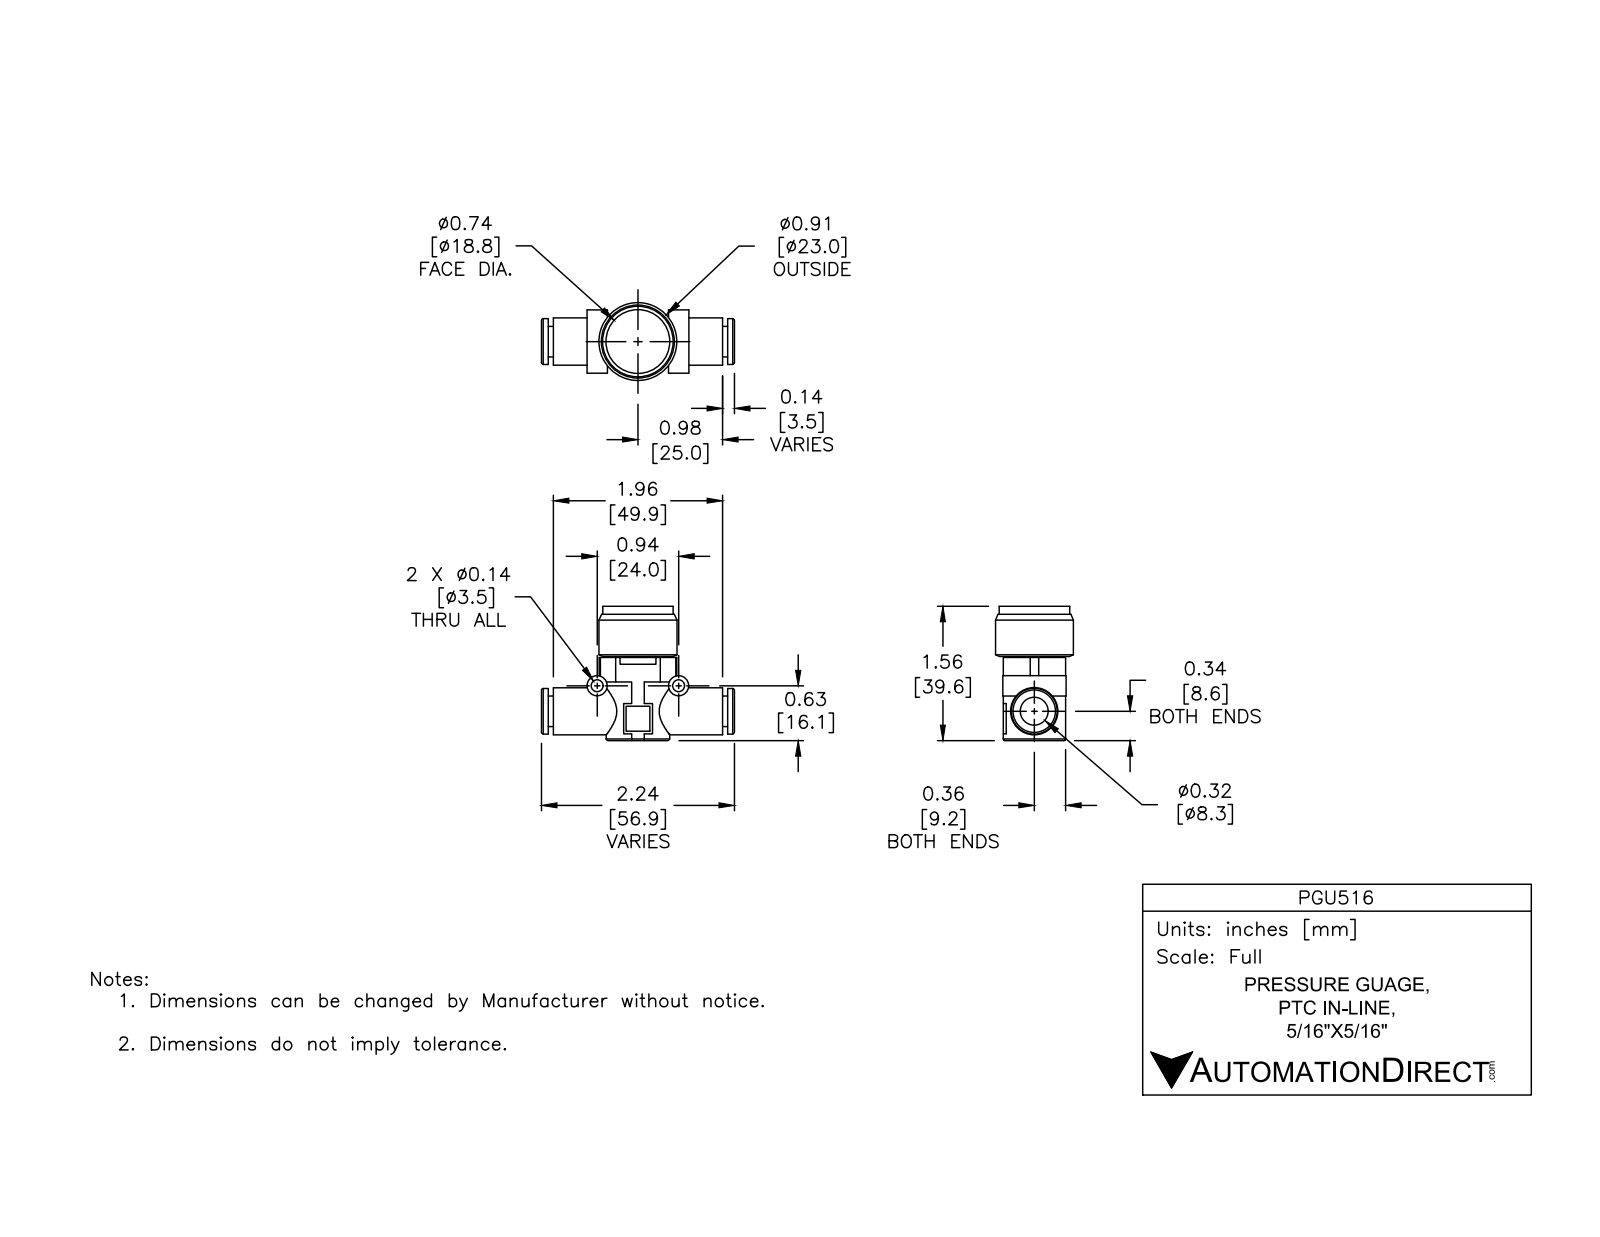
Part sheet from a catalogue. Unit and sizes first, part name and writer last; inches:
Units: inches
Overall size (bounding box): 2.24 × 1.559 × 0.906
Round holes (diameter × count): ⌀0.138 ×2, ⌀0.325 ×1, ⌀0.354 ×1, ⌀0.738 ×1, ⌀0.787 ×1, ⌀0.817 ×1
Round bosses / shafts (diameter × count): ⌀0.236 ×2, ⌀0.906 ×1, ⌀0.736 ×1, ⌀0.709 ×1, ⌀0.547 ×1, ⌀0.531 ×1, ⌀0.394 ×1, ⌀0.138 ×1
Partial cylindrical surfaces — rounded edges, fillets, slot ends (radius × count): R0.02 ×2, R0.098 ×2, R0.209 ×2, R0.039 ×1, R0.167 ×1
Main face-to-face distances: 0.079, 0.02, 0.059, 0.109, 0.09, 0.169, 0.232, 0.172, 0.153, 0.063
Hole centre spacings: 0.945
Volume: 0.956 in³ · Surface area: 16.75 in²
Bodies: 34 solids, 354 faces (232 planar, 63 cylindrical, 59 other)
Part name (STEP PRODUCT): PGU516
STEP written by: SolidWorks 2015 (CONFIG_CONTROL_DESIGN)
